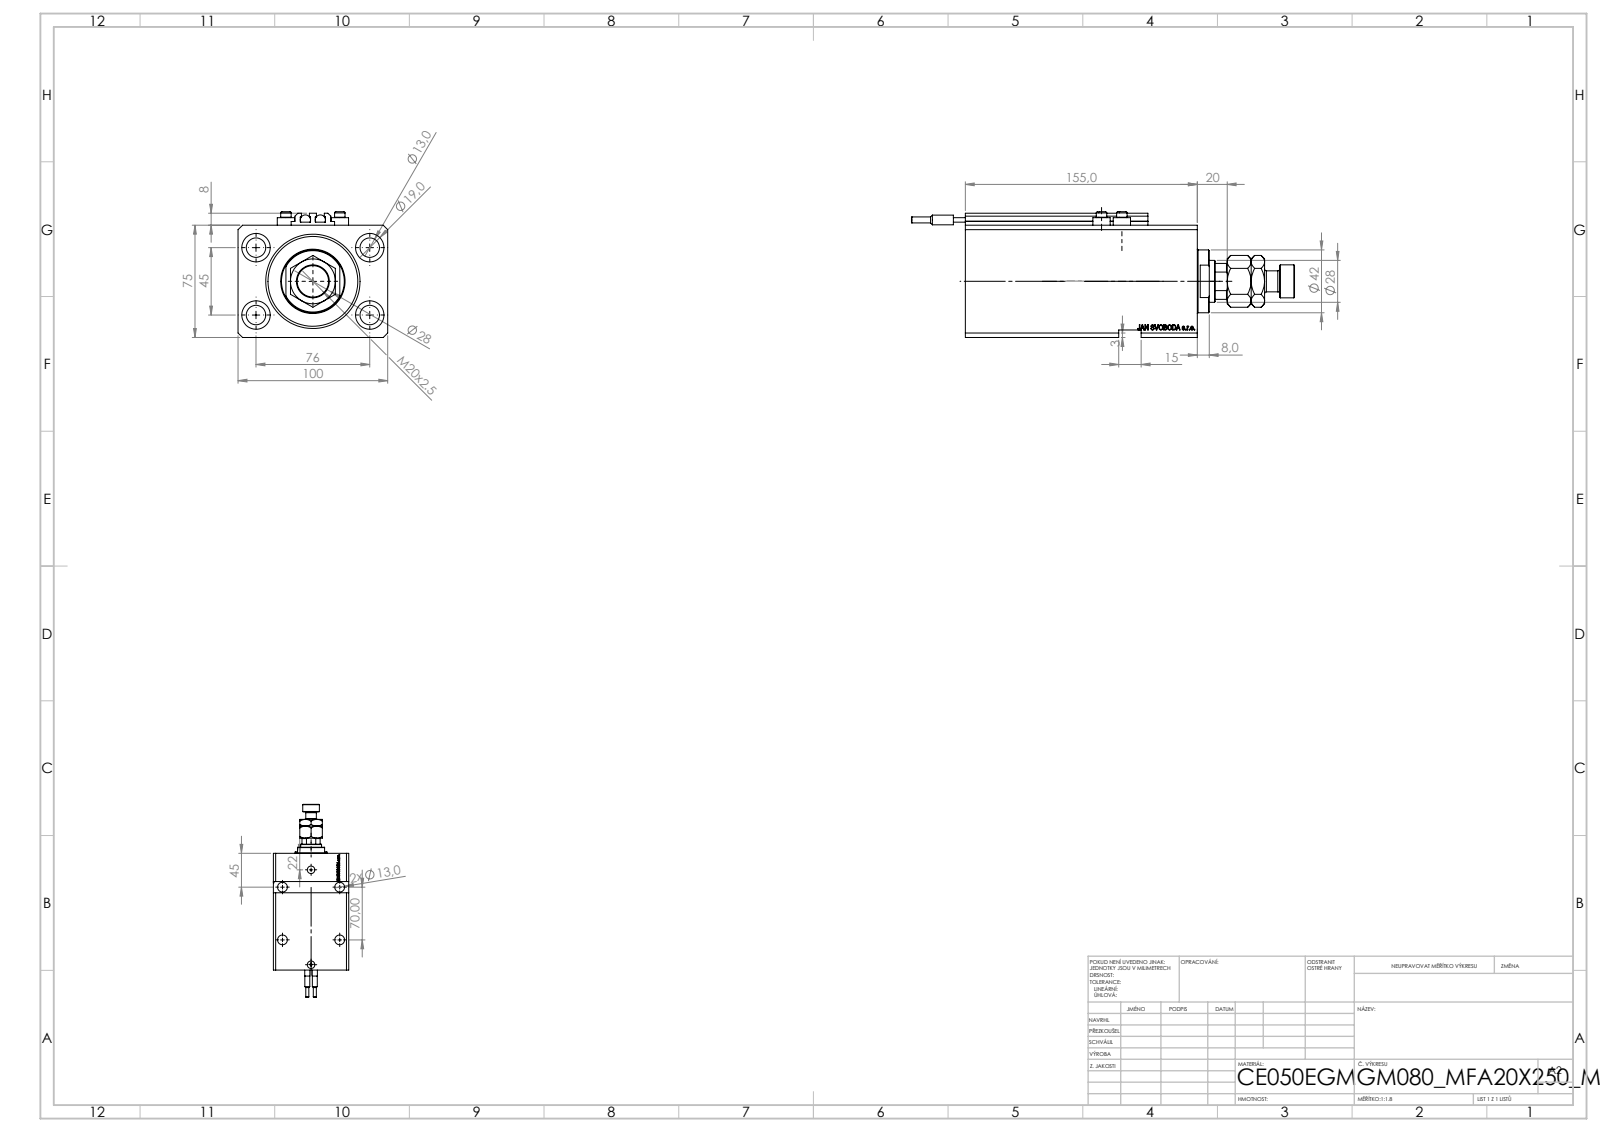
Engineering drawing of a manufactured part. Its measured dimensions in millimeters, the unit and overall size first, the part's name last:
Units: millimetres
Overall size (bounding box): 256 × 100 × 84
Round holes (diameter × count): ⌀13 ×8, ⌀1.25 ×4, ⌀4 ×4, ⌀19 ×4, ⌀10 ×2, ⌀13.16 ×2, ⌀20 ×2, ⌀18.5 ×1, ⌀28 ×1, ⌀50 ×1, ⌀63 ×1
Round bosses / shafts (diameter × count): ⌀11.6 ×4, ⌀7 ×4, ⌀6.8 ×2, ⌀6.5 ×2, ⌀4 ×2, ⌀42 ×1, ⌀22 ×1, ⌀14 ×1
Partial cylindrical surfaces — rounded edges, fillets, slot ends (radius × count): R0.2 ×10, R13.5 ×1
Main face-to-face distances: 75, 100, 20, 155, 11.9, 143.1, 135, 123.1, 3, 80
Hole centre spacings: 44.16, 76, 13.6, 20.72, 27.59, 33.62, 36, 38.48
Volume: 968 905 mm³ · Surface area: 184 255 mm²
Bodies: 11 solids, 1212 faces (583 planar, 162 cylindrical, 467 other)
Part name (STEP PRODUCT): MFA; V250CE_C_VCP; SWITCH_V250CE; ALLEN BOLT V250CE (+2 more)
STEP written by: SolidWorks 2019 (CONFIG_CONTROL_DESIGN)
